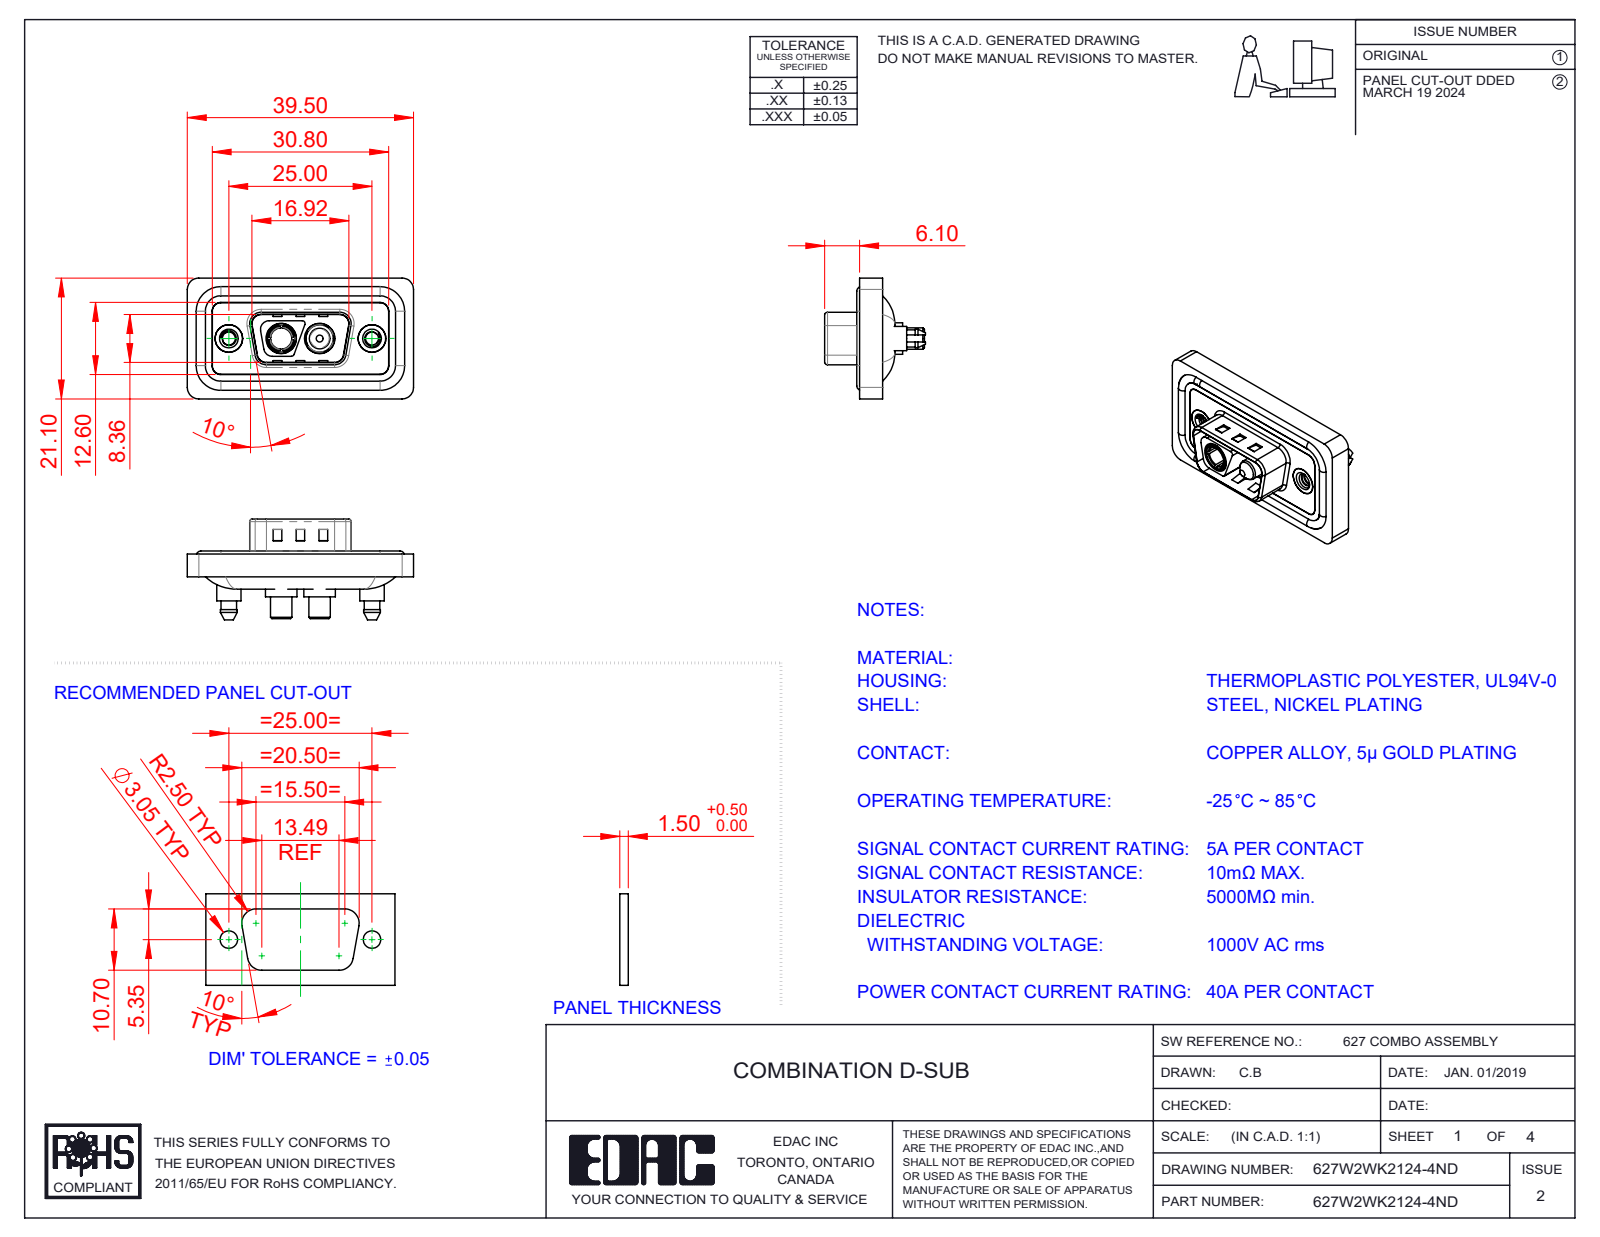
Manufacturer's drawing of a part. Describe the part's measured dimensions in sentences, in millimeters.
The part is named "Power Pin_40A S; Power Socket_40A S; 627Combo Shell Rear_09 Contacts; 627W2WK2124-4ND (+5 more)". Its 3-D file was written by "SolidWorks 2023 (CONFIG_CONTROL_DESIGN)". It is 11 solids with 592 faces: 205 planar, 267 cylindrical and 120 other. Overall it measures 39.5 by 21.1 by 17.6 millimeters. Its volume is 4 726 cubic millimeters and its surface area 7 700 square millimeters. Round holes: 2 of diameter 2.26, 2 of diameter 4, 2 of diameter 4.8, 2 of diameter 4.85, 2 of diameter 5, 2 of diameter 5.3, 1 of diameter 3.7. Round bosses or shafts: 4 of diameter 1.6, 2 of diameter 5.5, 2 of diameter 5.4, 2 of diameter 5.2, 2 of diameter 4.9, 2 of diameter 4.75, 2 of diameter 4.25, 2 of diameter 3.75. Partial cylindrical surfaces (rounded edges, fillets, slot ends): 26 of radius 1.5, 18 of radius 2, 10 of radius 0.5, 10 of radius 1.6, 4 of radius 0.25, 4 of radius 0.6, 4 of radius 0.65, 4 of radius 0.9. The main face-to-face distances are 0.4, 1.1, 2.9, 3.1, 0.5, 1.6, 1.5, 4, 1.8, 3.2. The hole center spacings are 9.14, 15.86, 6.72, 25.
